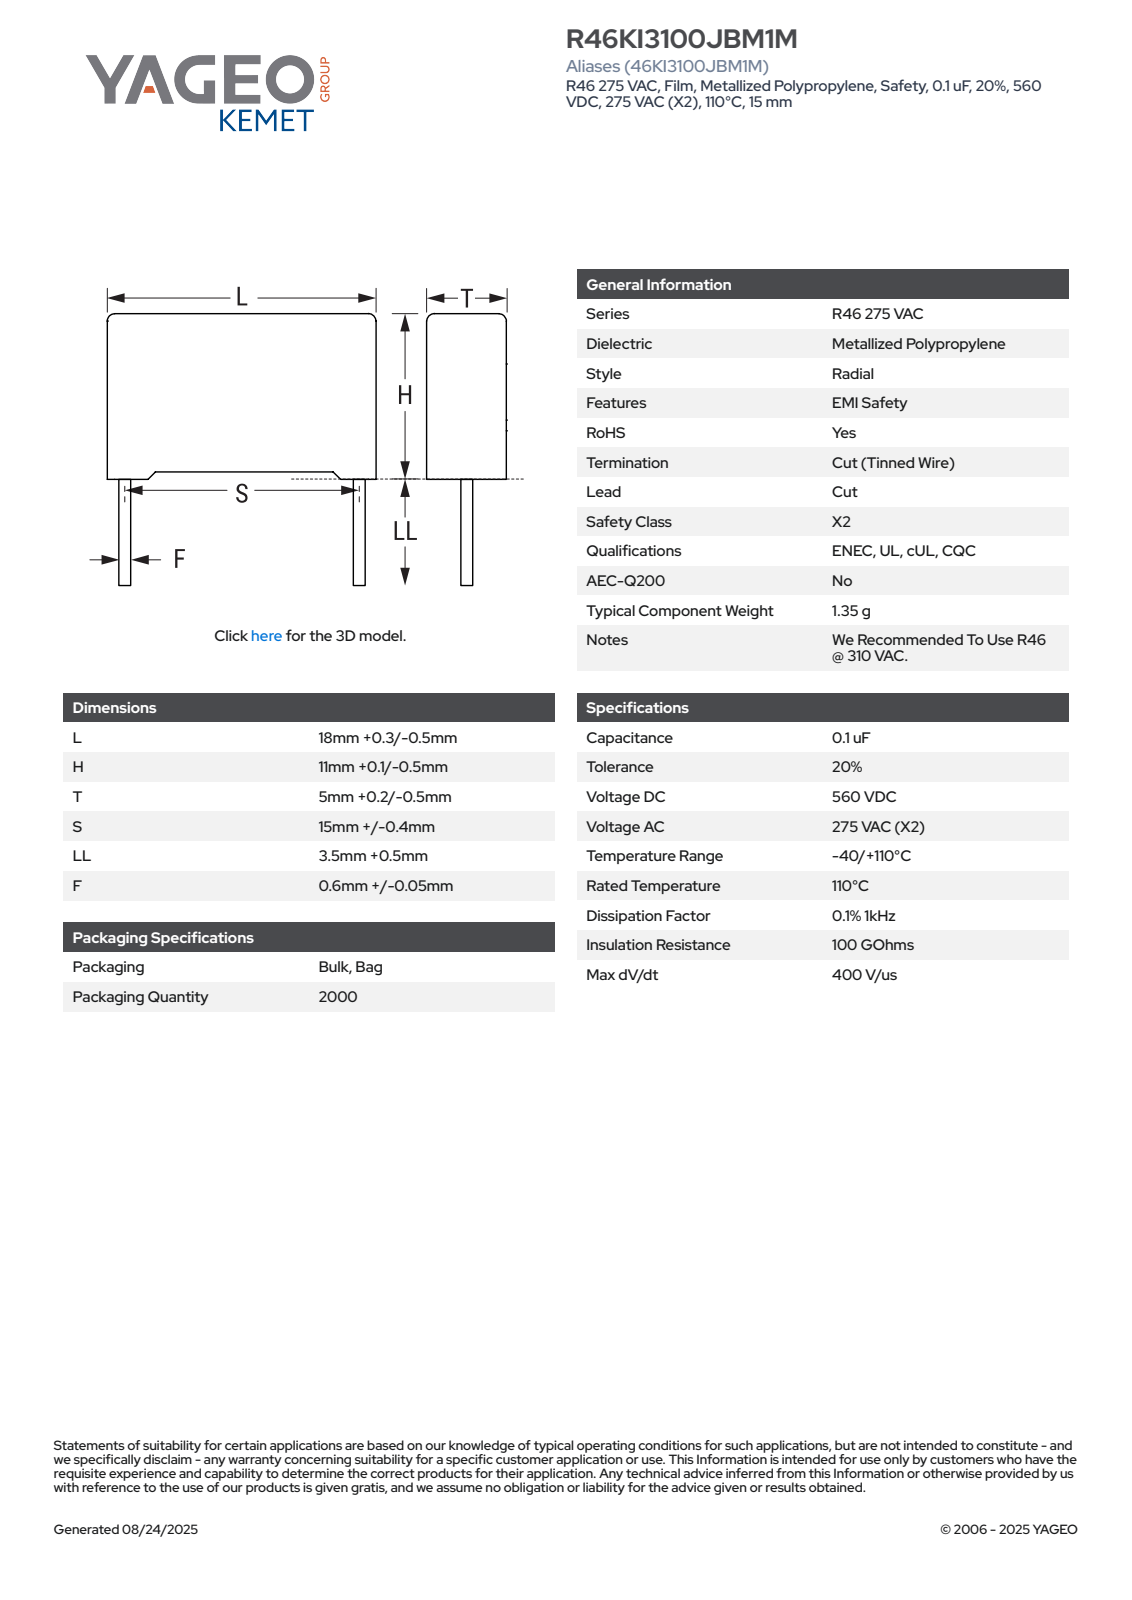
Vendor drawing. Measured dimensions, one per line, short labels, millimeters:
name: CFR_RB2_18X11X5_L18.3H11.1T5.2S15LL4F0.65
written by: SolidWorks 2021 (AUTOMOTIVE_DESIGN)
unit: mm
bodies: 4 solids, 85 faces (77 planar, 8 cylindrical, 0 other)
size: 18.3 × 15.1 × 5.21
volume: 1 001 mm³; area: 761 mm²
bosses: 2× ⌀0.65
rounds: 4× R0.5
face distances: 5.2, 10.35, 18.3, 0.61, 4.59, 0.37, 10.72, 0.38, 0.75, 11.1
